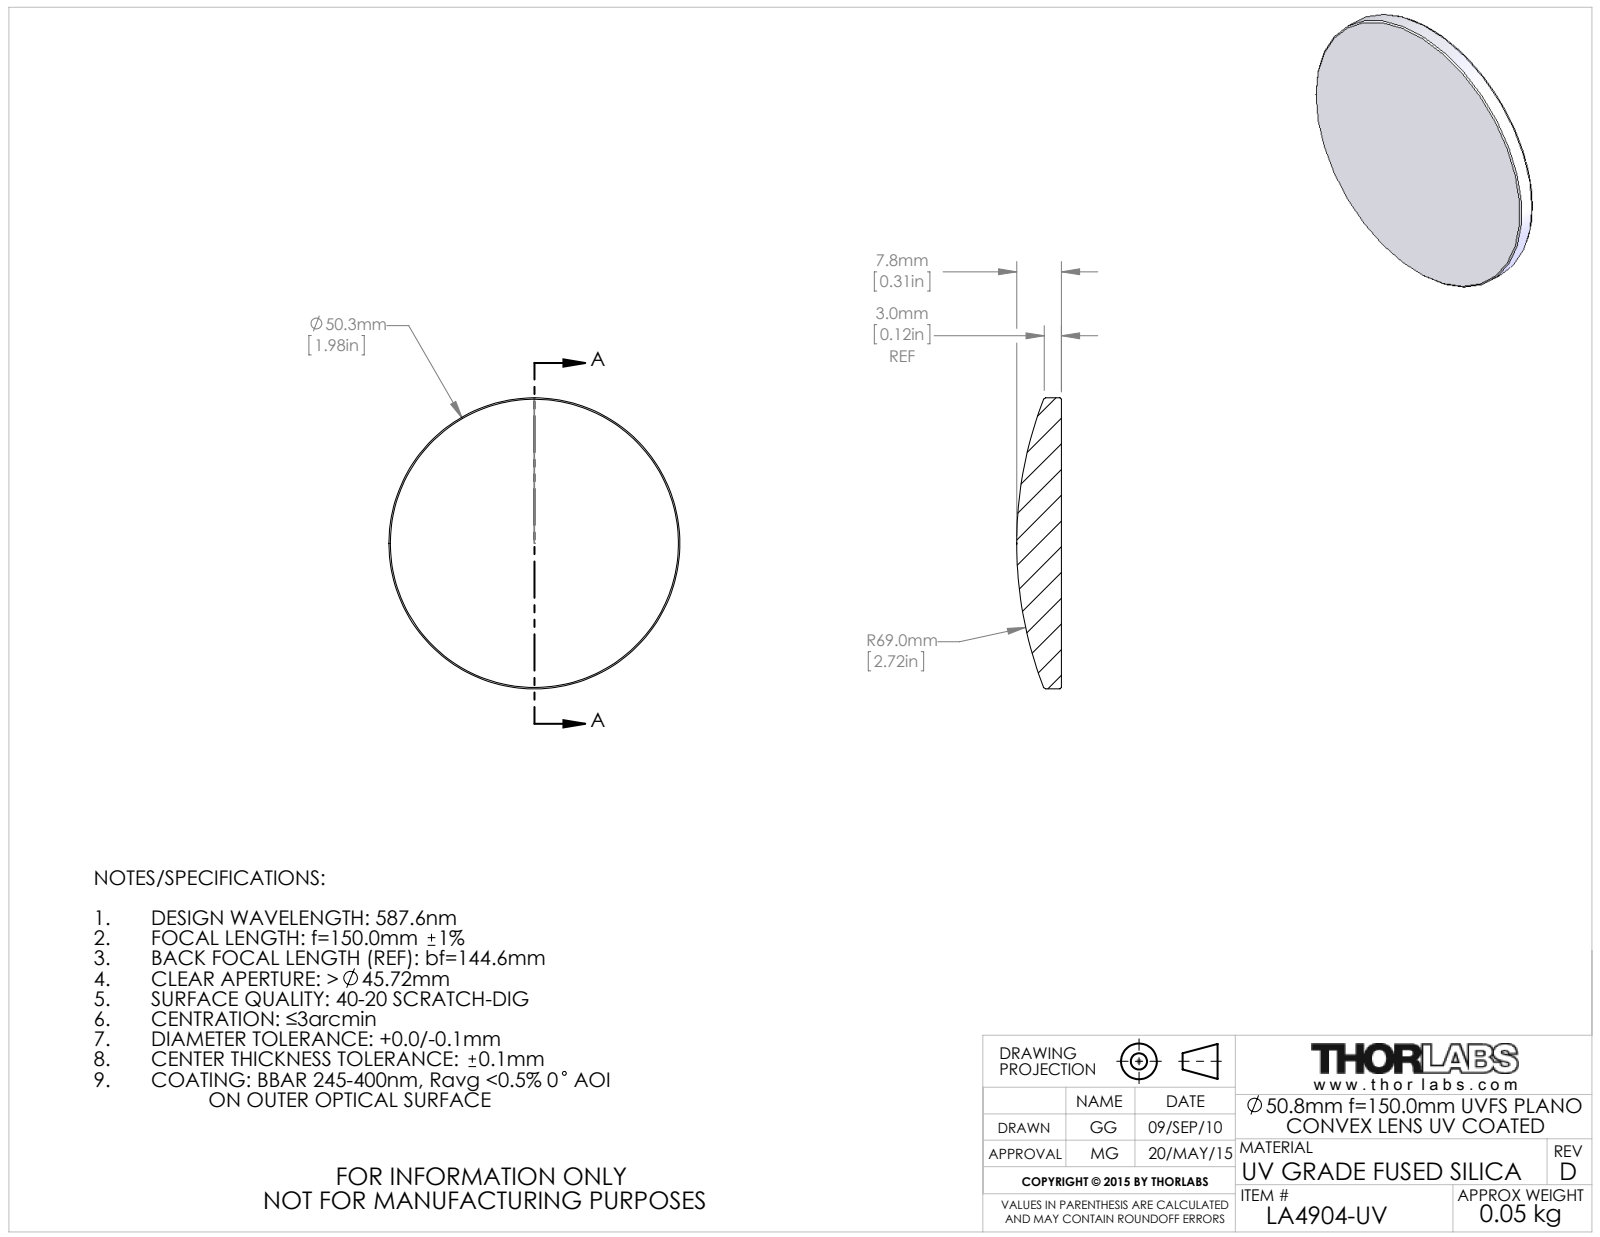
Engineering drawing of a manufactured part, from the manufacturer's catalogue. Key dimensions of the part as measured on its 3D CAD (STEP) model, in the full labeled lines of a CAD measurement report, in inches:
Part name (STEP PRODUCT): 4295-E0W
STEP written by: SolidWorks 2014 (CONFIG_CONTROL_DESIGN)
Units: inches
Bodies: 1 solid, 9 faces (1 planar, 2 cylindrical, 6 other)
Overall size (bounding box): 2 × 2 × 0.307
Volume: 0.672 in³ · Surface area: 7.08 in²
Round bosses / shafts (diameter × count): ⌀2 ×1
